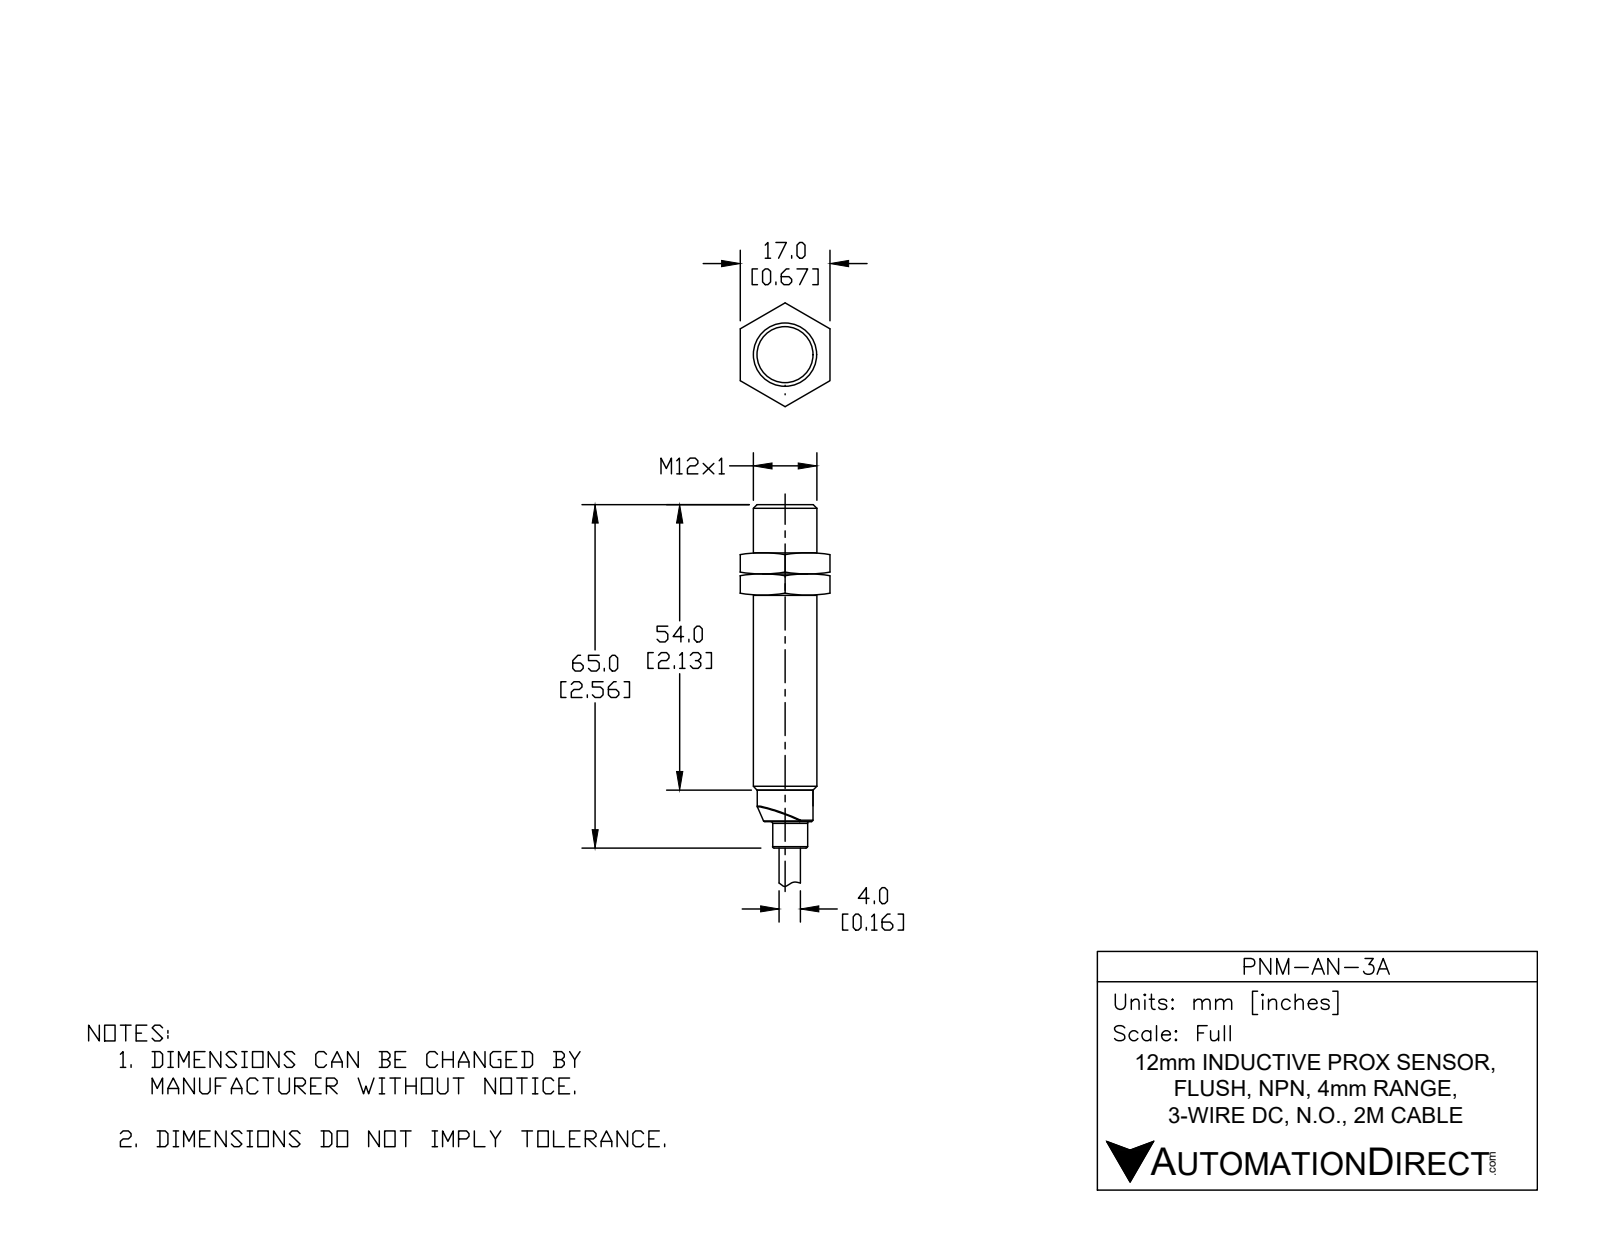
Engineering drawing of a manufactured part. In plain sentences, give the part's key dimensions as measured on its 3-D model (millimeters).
The part is named "PNM-AN-3A". Its 3-D file was written by "SolidWorks 2017 (AUTOMOTIVE_DESIGN)". It is 1 solid with 68 faces: 21 planar, 19 cylindrical and 28 other. Overall it measures 115.8 by 12 by 12 millimeters. Its volume is 7 410 cubic millimeters and its surface area 3 208 square millimeters. Round holes: 1 of diameter 4.1, 1 of diameter 10.2. Round bosses or shafts: 1 of diameter 12, 1 of diameter 10.6, 1 of diameter 10.5, 1 of diameter 9.8, 1 of diameter 6.6, 1 of diameter 4. Partial cylindrical surfaces (rounded edges, fillets, slot ends): 1 of radius 2.3. The main face-to-face distances are 60, 65, 5, 115.8, 55.8, 50.8, 0.6, 59.4, 64.4, 115.2. The hole center spacings are 1.
